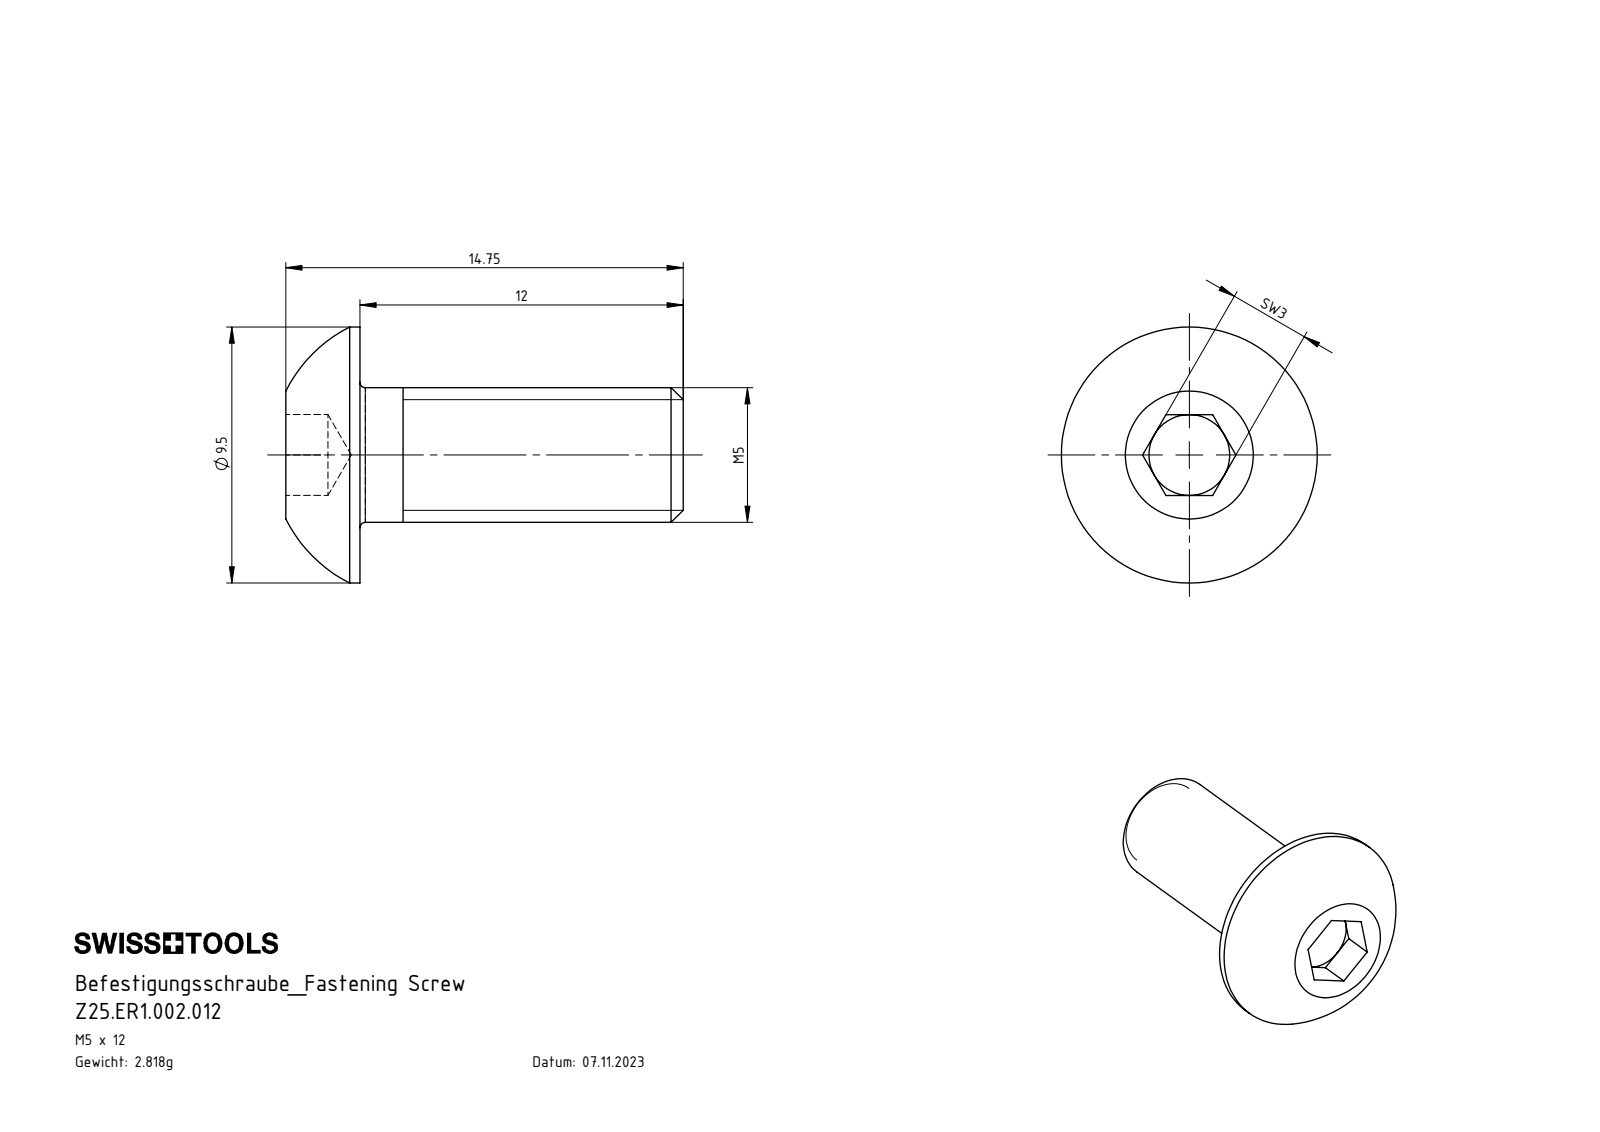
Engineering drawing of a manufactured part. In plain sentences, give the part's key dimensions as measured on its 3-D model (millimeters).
The part is named "Z25.ER1.002.012". Its 3-D file was written by "SolidWorks 2017 (AUTOMOTIVE_DESIGN)". It is 1 solid with 27 faces: 15 planar, 4 cylindrical and 8 other. Overall it measures 14.75 by 9.5 by 9.5 millimeters. Its volume is 359 cubic millimeters and its surface area 379 square millimeters. Round bosses or shafts: 1 of diameter 9.5, 1 of diameter 5. The main face-to-face distances are 12, 2.75, 14.75, 3, 1.56, 1.19, 13.19.
